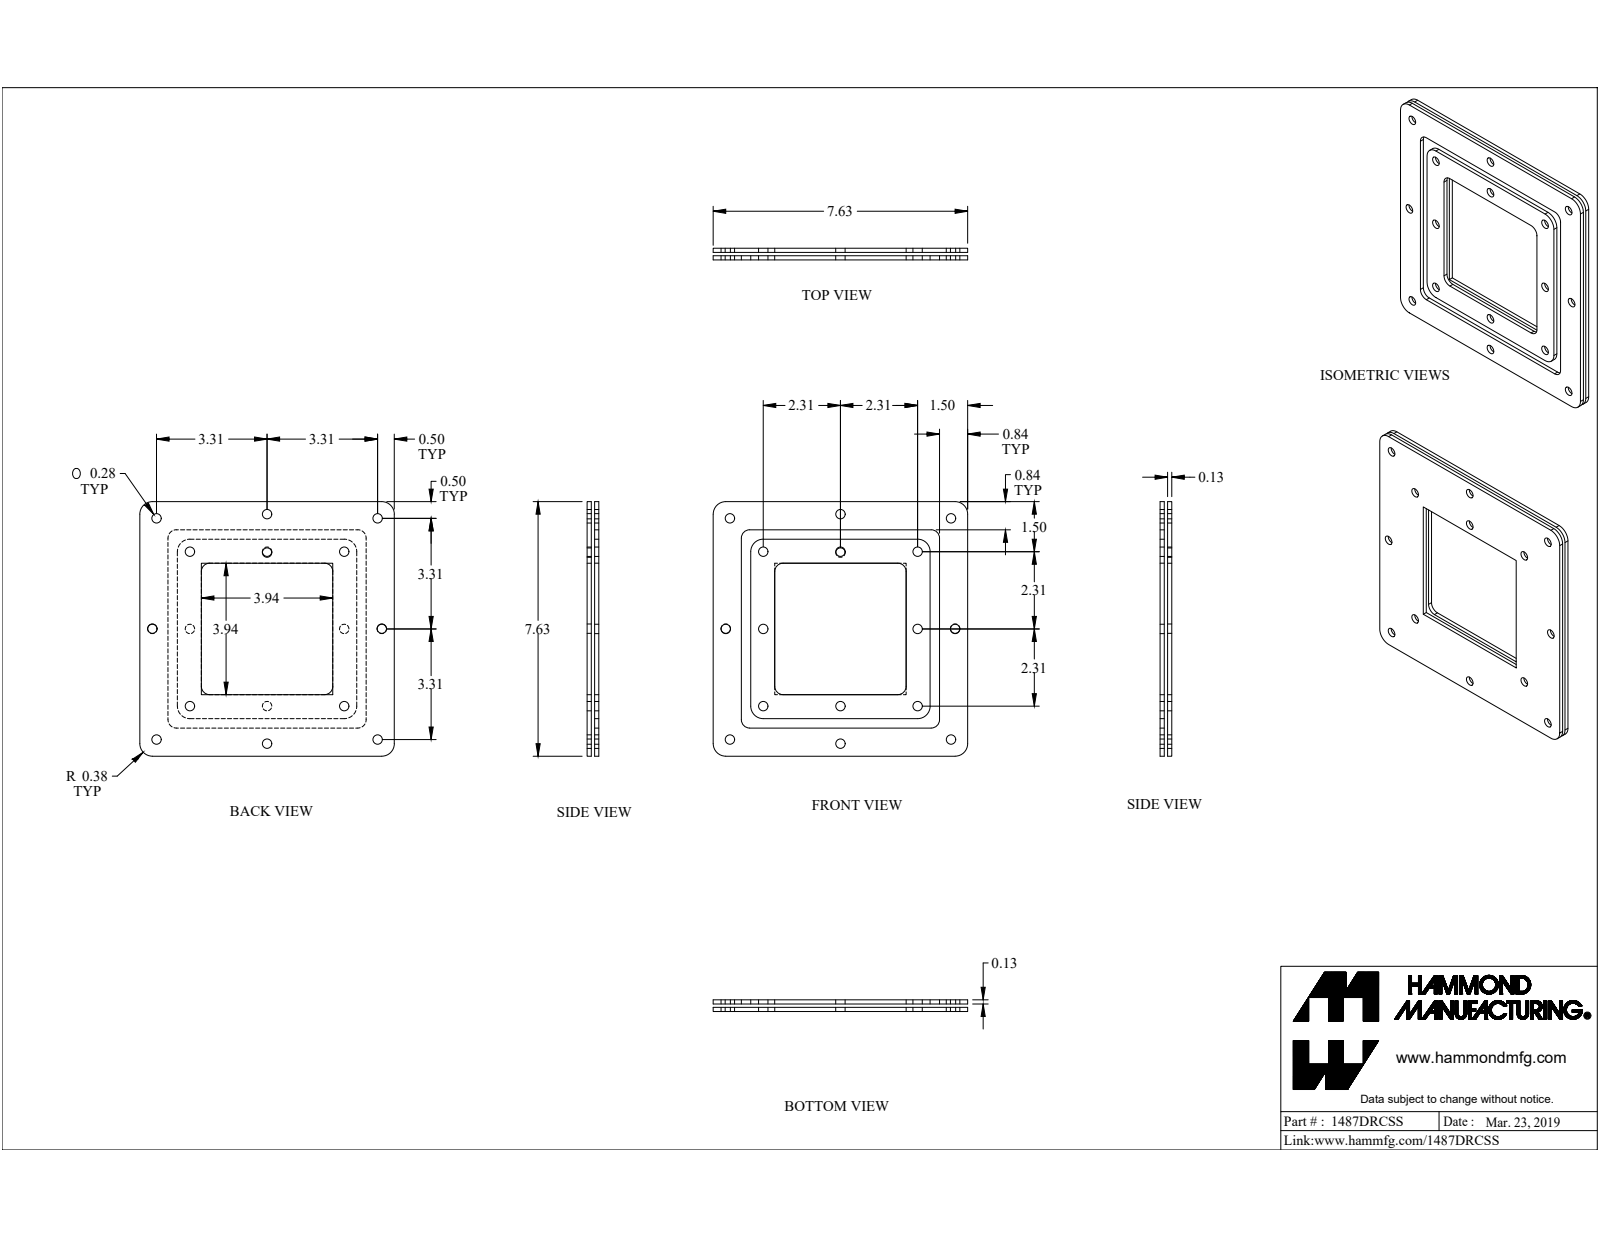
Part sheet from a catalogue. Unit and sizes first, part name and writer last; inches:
Units: inches
Overall size (bounding box): 7.625 × 7.625 × 0.971
Round holes (diameter × count): ⌀0.281 ×19, ⌀0.196 ×2, ⌀0.258 ×2, ⌀0.35 ×2
Round bosses / shafts (diameter × count): ⌀0.5 ×2, ⌀0.25 ×2
Partial cylindrical surfaces — rounded edges, fillets, slot ends (radius × count): R0.02 ×12, R0.25 ×8, R0.375 ×8
Main face-to-face distances: 0.125, 0.225, 0.35, 0.125, 0.1, 0.225, 0.1, 7.625, 6.782, 0.843
Hole centre spacings: 2.313, 2.572, 3.315, 3.46, 4.143, 5.171, 5.713, 6.198
Volume: 9.785 in³ · Surface area: 178.3 in²
Bodies: 9 solids, 253 faces (144 planar, 93 cylindrical, 16 other)
Part name (STEP PRODUCT): 1487DRCSS
STEP written by: SolidWorks 2019 (CONFIG_CONTROL_DESIGN)
